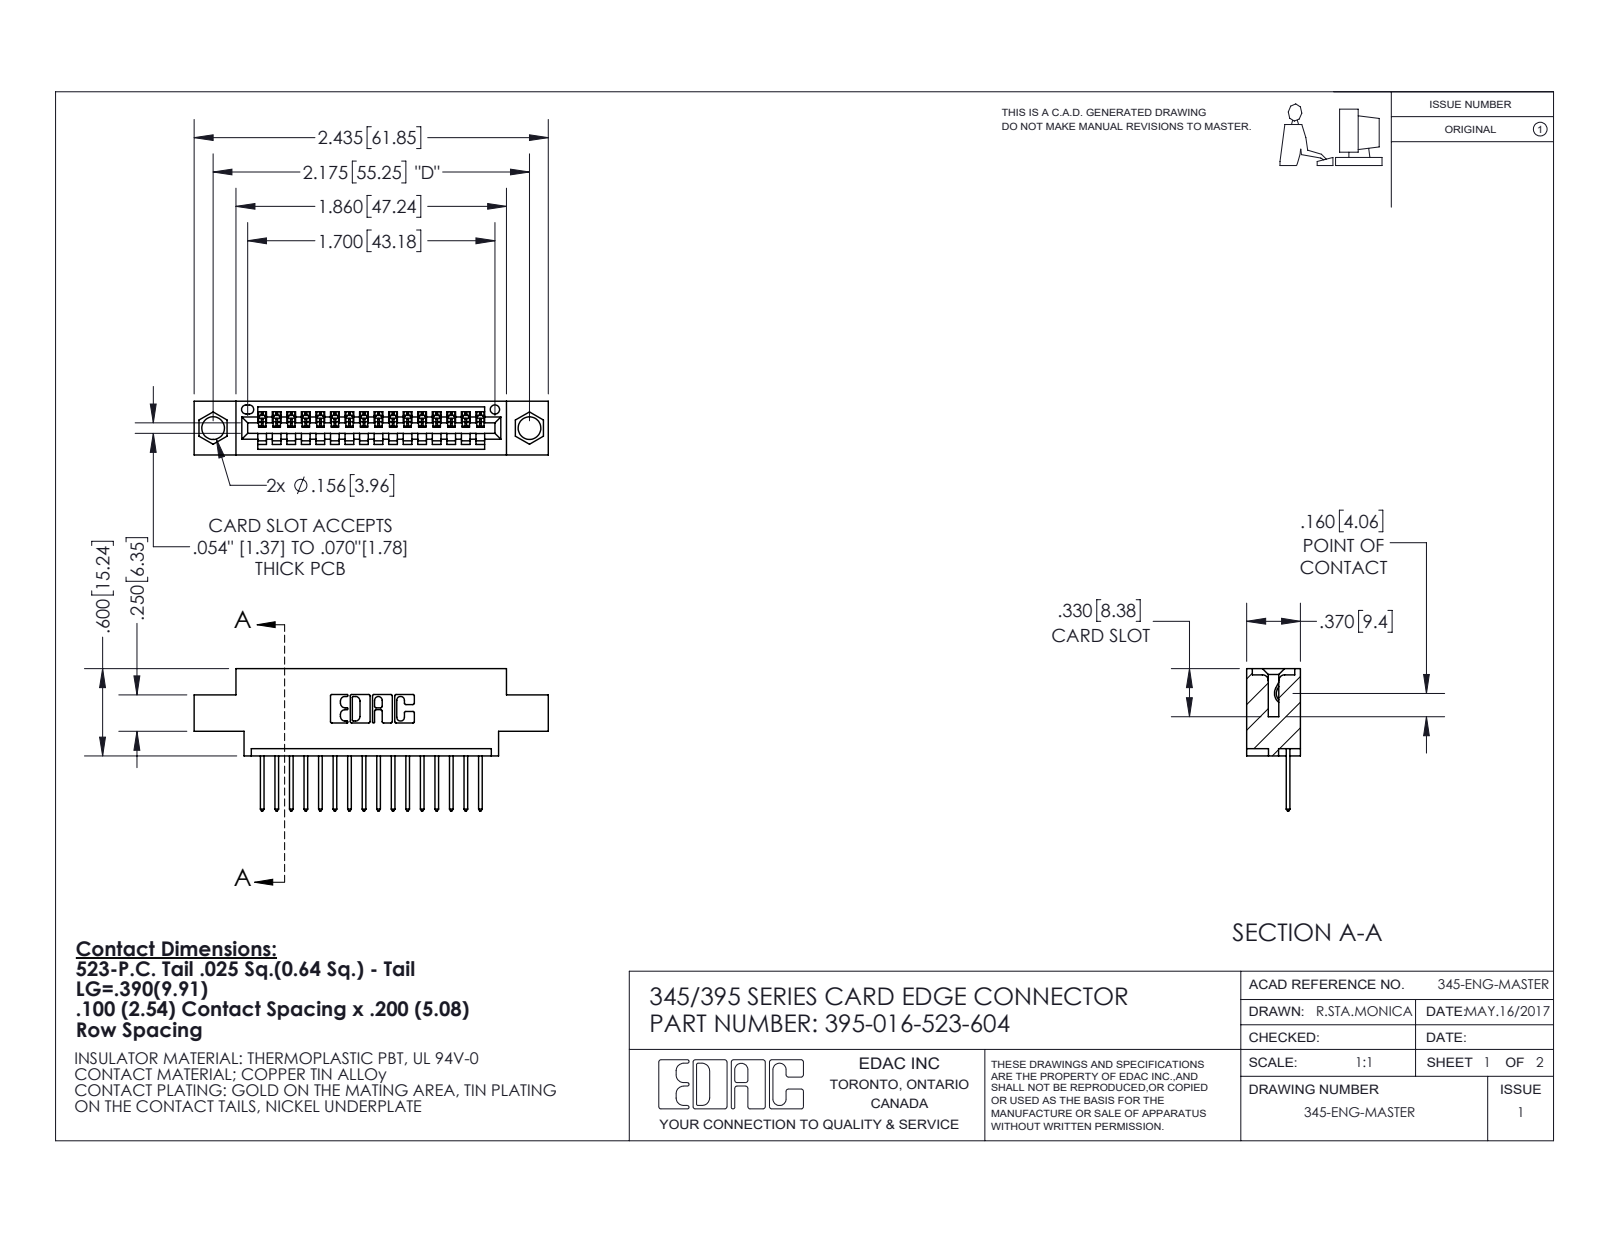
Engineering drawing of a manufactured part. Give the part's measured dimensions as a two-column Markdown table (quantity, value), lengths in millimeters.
| quantity | value |
| --- | --- |
| part name | 395-016-523-604; 345 Part_0.170 Offset - 0.156 Dia-TI; 345-292-001_345-293-123 |
| STEP written by | SolidWorks 2020 (CONFIG_CONTROL_DESIGN) |
| units | millimeters |
| bodies | 17 solids, 1072 faces (738 planar, 334 cylindrical, 0 other) |
| overall size | 61.8 × 24.8 × 9.4 |
| volume | 5 440 mm³ |
| surface area | 6 858 mm² |
| round holes (diameter × count) | 4 × 2, 1.6 × 1 |
| partial cylindrical surfaces (radius × count) | 0.2 × 32, 0.3 × 32, 0.3 × 22, 0.2 × 6, 0.8 × 6, 0.7 × 3, 0.8 × 2, 1 × 2 |
| main face-to-face distances | 1.8, 7.6, 9.4, 5.1, 2.5, 6.9, 0.6, 2.5, 5.7, 3.8 |
| hole center spacings | 6.9, 49.3, 55.2 |
